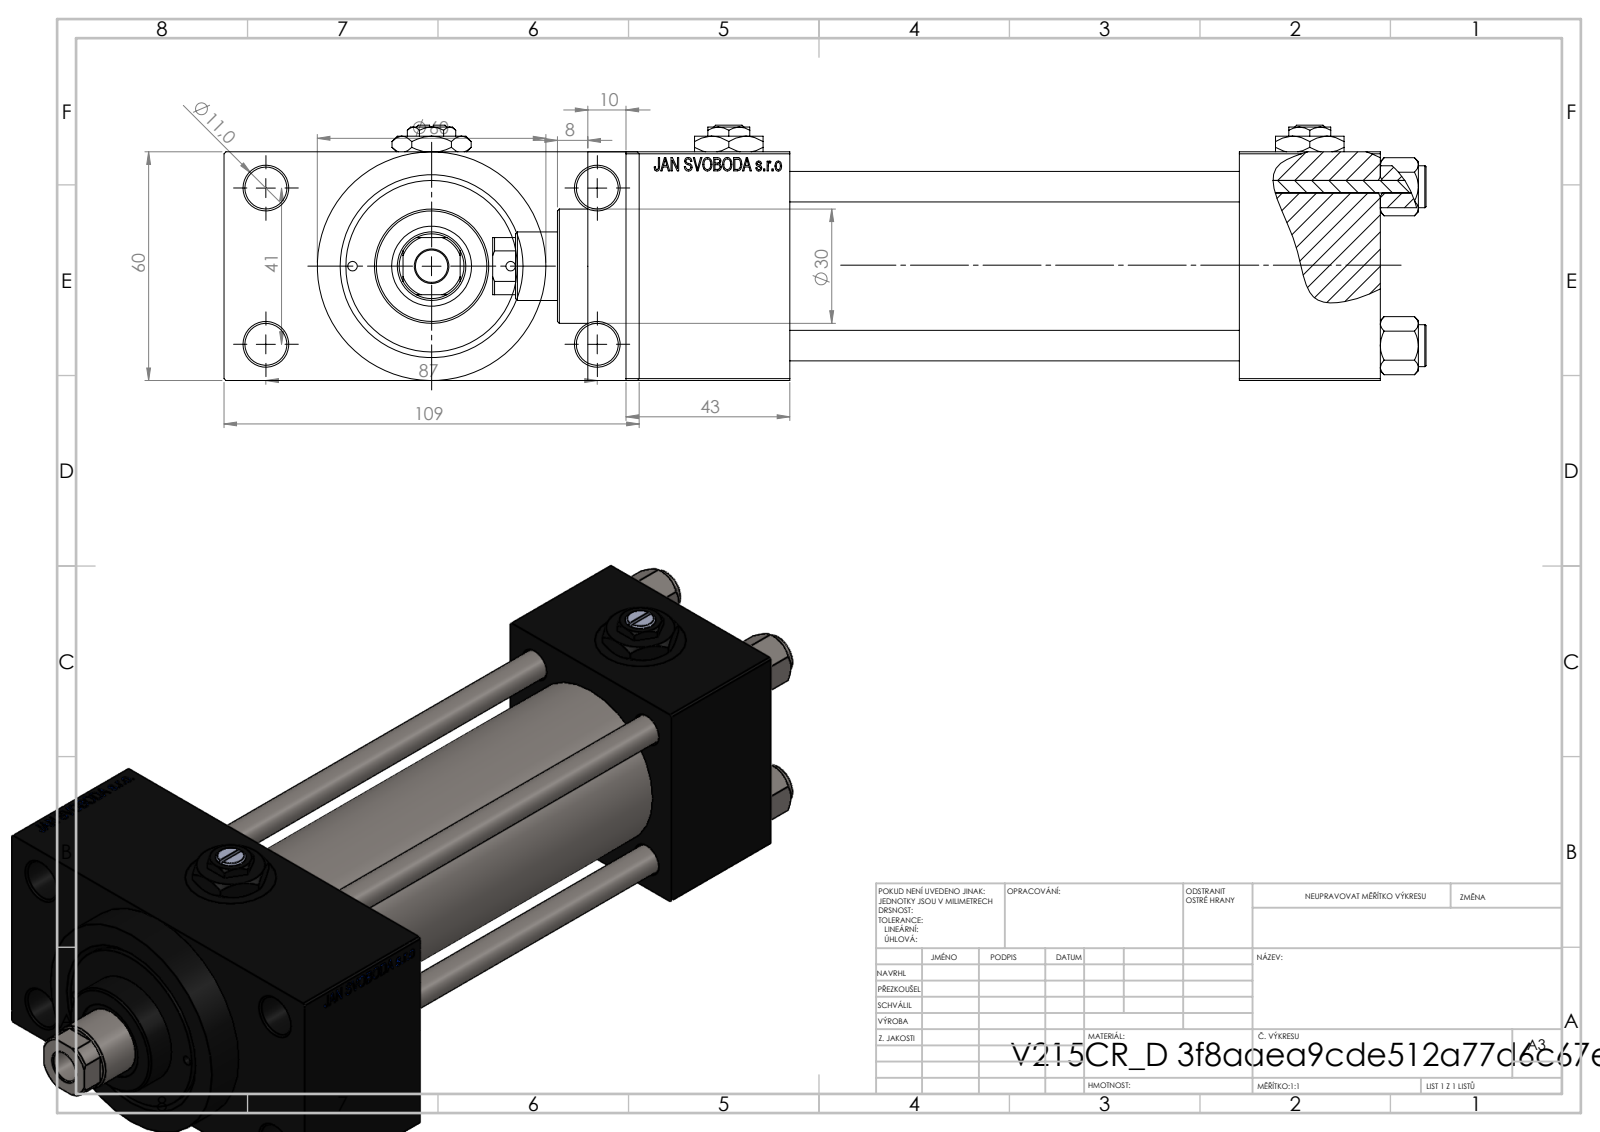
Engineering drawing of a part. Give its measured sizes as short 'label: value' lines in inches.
name: V215CR_D_Body; Zatka_pro_OIL_PORT; NUT_M5_D; V215CR_D_TYCINKA (+2 more)
written by: SolidWorks 2019 (CONFIG_CONTROL_DESIGN)
unit: in
bodies: 13 solids, 1214 faces (548 planar, 104 cylindrical, 562 other)
size: 9.646 × 4.291 × 2.638
volume: 34.6 in³; area: 231.7 in²
holes: 4× ⌀0.315, 4× ⌀0.433, 2× ⌀0.098, 2× ⌀0.276, 2× ⌀0.656, 2× ⌀0.945, 1× ⌀0.335, 1× ⌀0.709, 1× ⌀0.827, 1× ⌀1.22, 1× ⌀1.575, 1× ⌀1.772
bosses: 4× ⌀0.433, 1× ⌀2.362, 1× ⌀1.811, 1× ⌀1.181
rounds: 1× R0.335
face distances: 2.362, 0.965, 3.327, 4.646, 1.457, 6.102, 1.693, 7.795, 6.339, 4.291
hole spacings: 0.821, 0.892, 1.161, 1.206, 1.642, 1.832, 1.856, 1.893
